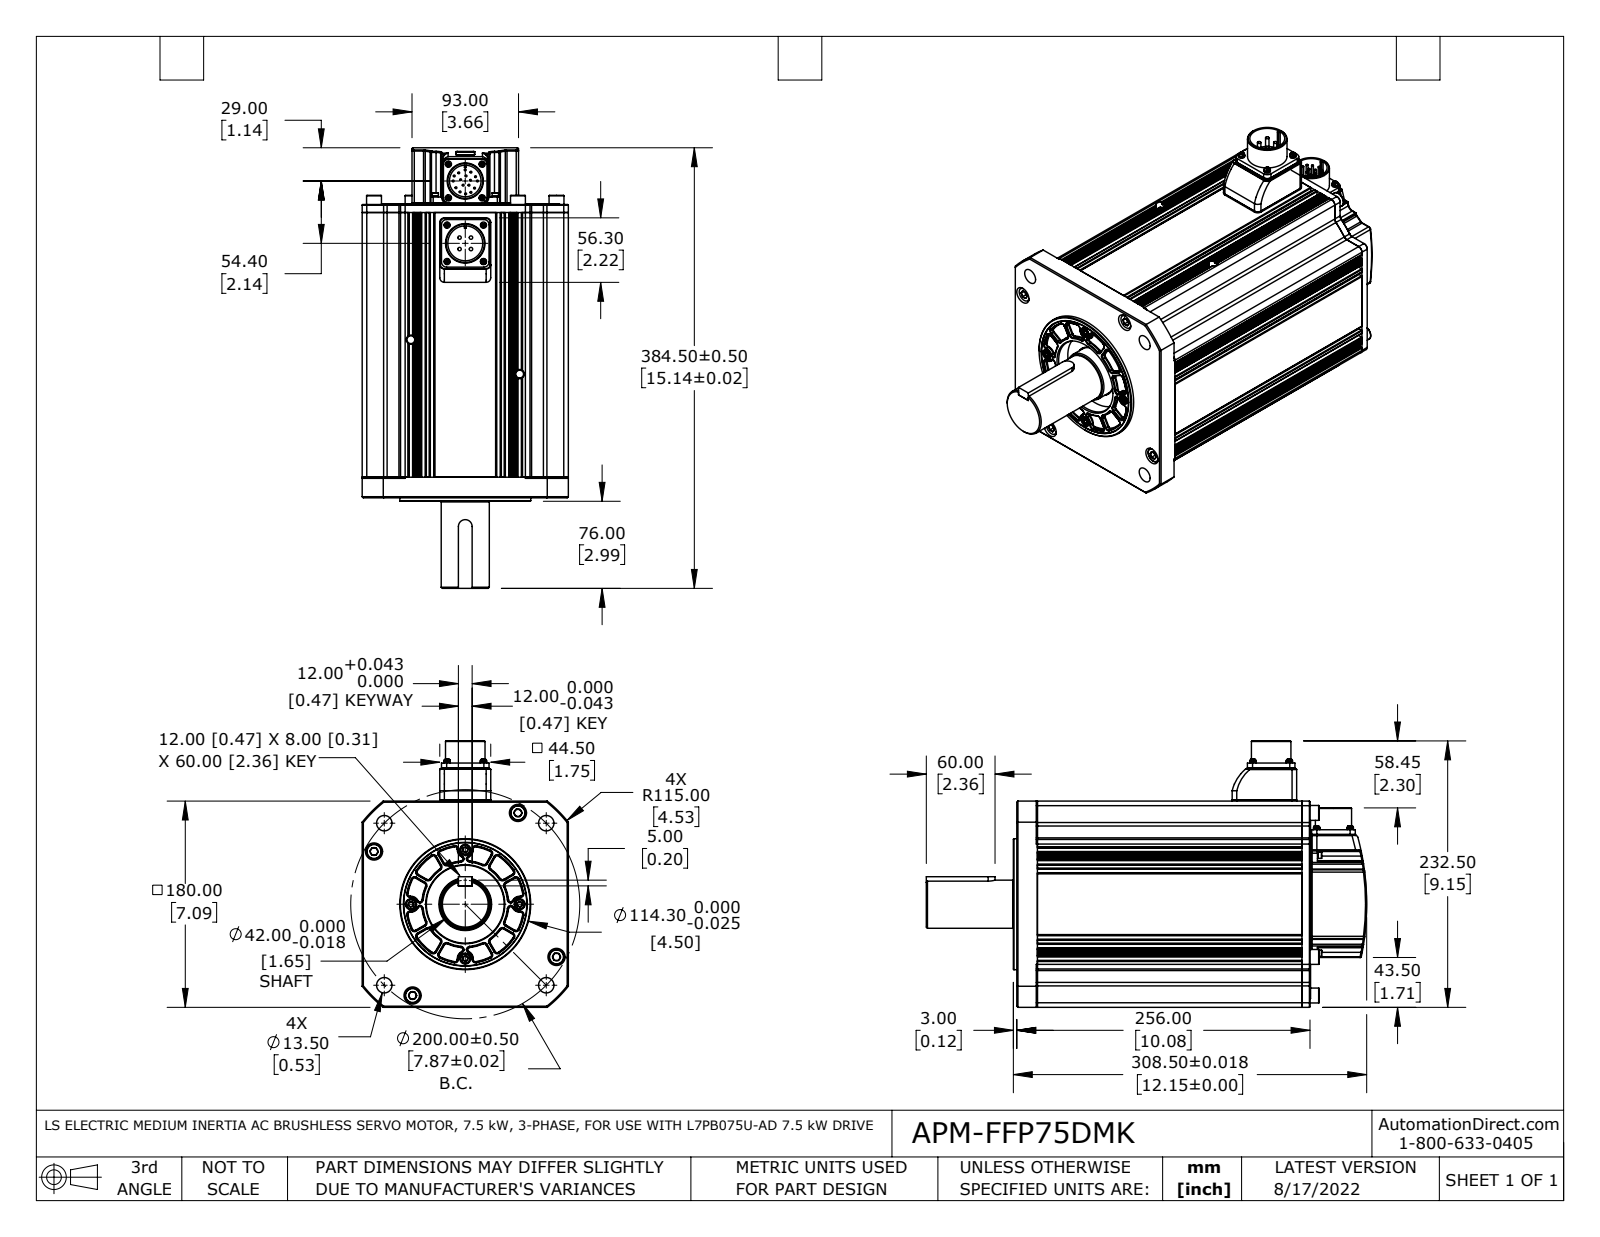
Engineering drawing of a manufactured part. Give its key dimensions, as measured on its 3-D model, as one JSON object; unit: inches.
{"part_name": "FMP18GA001G04_Out Line(APM-FFP75D_K) r1 nc fxt", "step_written_by": "SolidWorks 2017 (AUTOMOTIVE_DESIGN)", "units": "inches", "bodies": {"solids": 57, "faces": 2355, "planar": 795, "cylindrical": 874, "other": 686}, "overall_size": [15.138, 9.154, 7.087], "volume_in3": 472.3, "surface_area_in2": 873.9, "round_holes": [[0.118, 12], [0.098, 8], [0.12, 8], [0.236, 8], [0.374, 8], [0.268, 6], [0.138, 4], [0.142, 4], [0.146, 4], [0.197, 4], [0.354, 4], [0.362, 4]], "round_bosses_or_shafts": [[0.063, 17], [0.213, 8], [0.52, 4], [0.512, 4], [0.335, 4], [0.315, 4], [0.217, 4], [0.118, 4]], "partial_cylinders_radius": [[0.02, 124], [0.098, 56], [0.157, 24], [0.079, 17], [0.039, 14], [0.177, 12], [0.256, 4], [0.012, 2]], "face_to_face_distances": [9.094, 7.087, 0.039, 0.295, 0.709, 1.319, 5.768, 0.315, 0.394, 0.276], "hole_center_spacings": [1.282, 2.93, 5.423, 0.042, 0.819, 0.885, 0.927, 1.035]}
